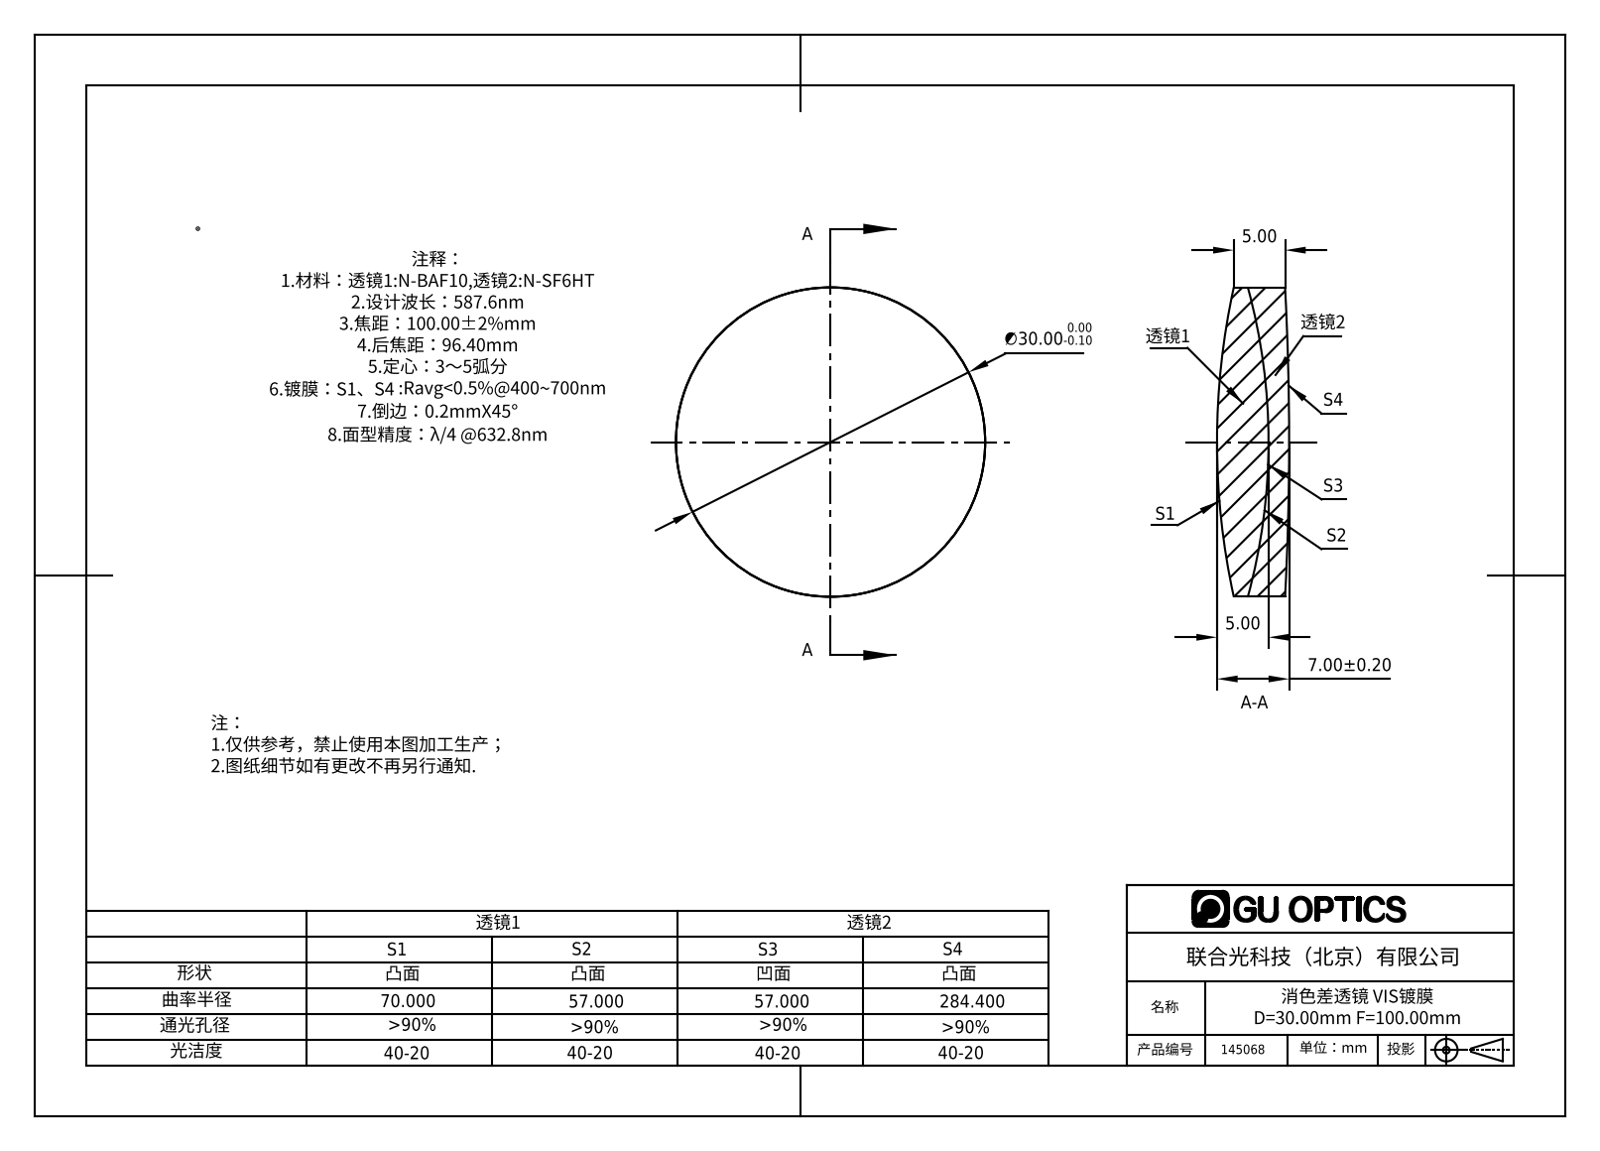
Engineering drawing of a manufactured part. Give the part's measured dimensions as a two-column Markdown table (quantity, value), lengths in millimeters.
| quantity | value |
| --- | --- |
| part name | 145068 |
| STEP written by | SolidWorks 2016 (AUTOMOTIVE_DESIGN) |
| units | millimeters |
| bodies | 2 solids, 12 faces (0 planar, 4 cylindrical, 8 other) |
| overall size | 30 × 30 × 7 |
| volume | 4 236 mm³ |
| surface area | 3 331 mm² |
| round bosses / shafts (diameter × count) | 30 × 1 |
